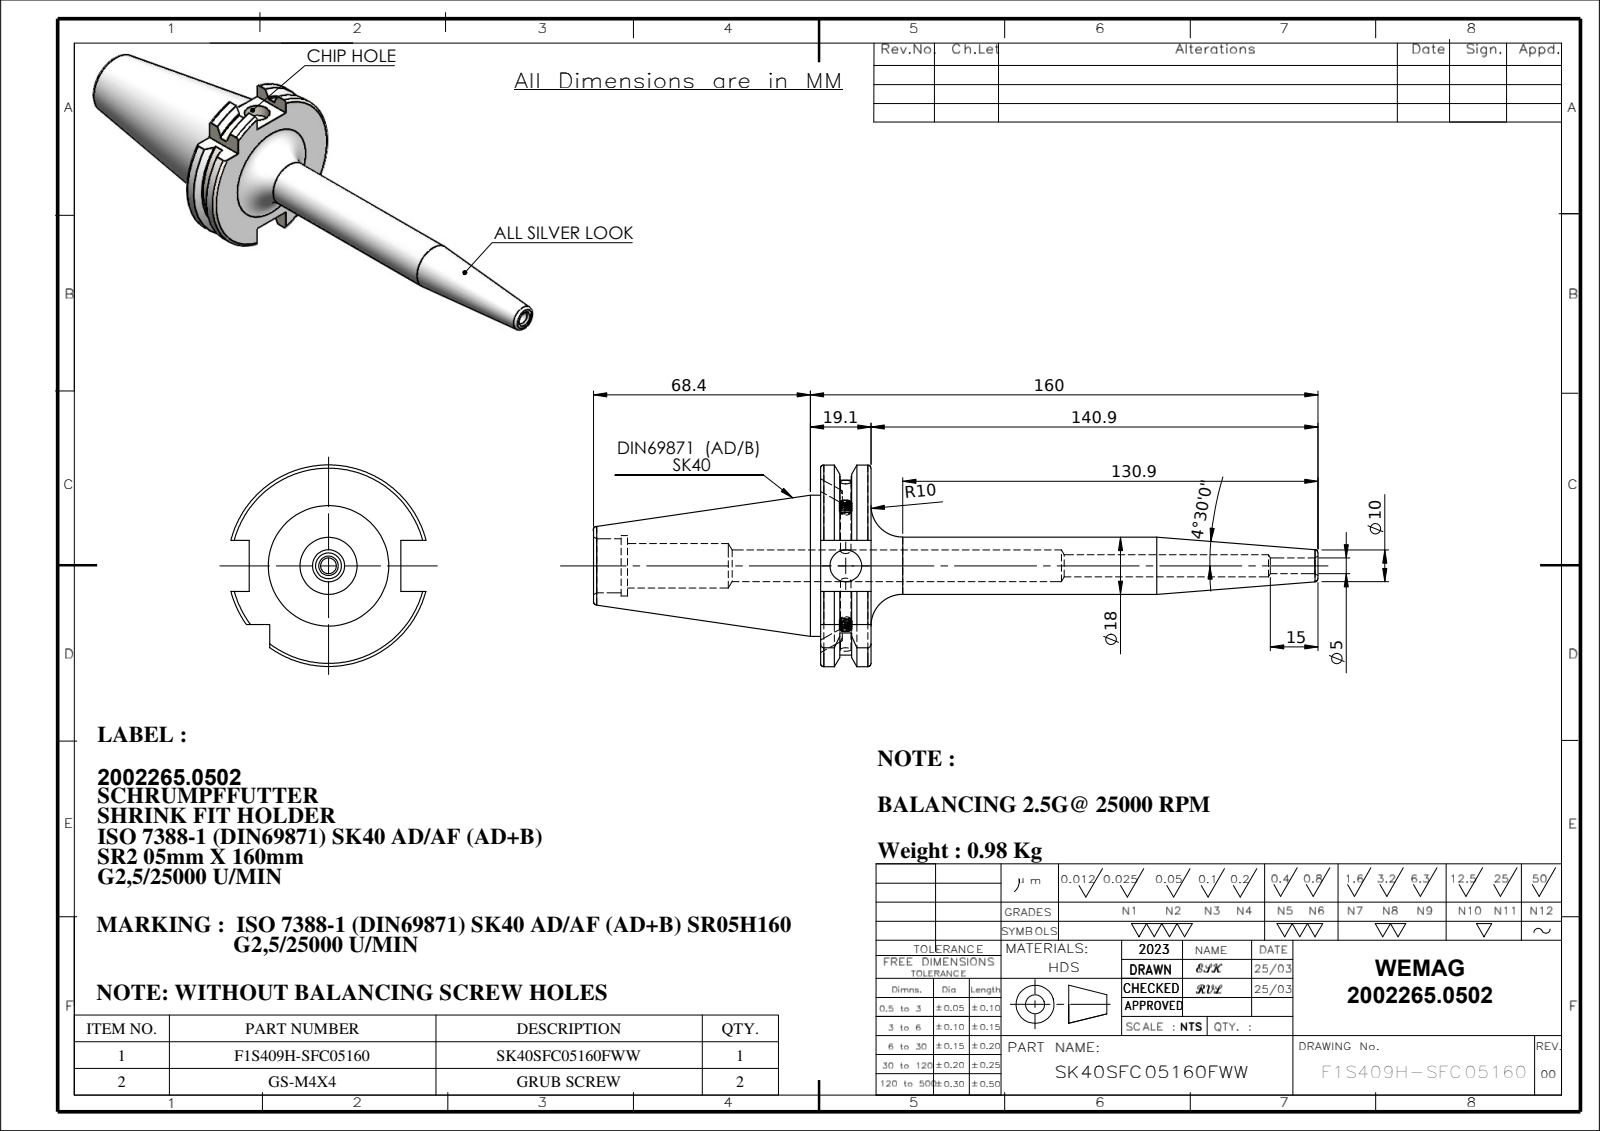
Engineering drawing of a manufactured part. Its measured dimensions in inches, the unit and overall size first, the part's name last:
Units: inches
Overall size (bounding box): 8.992 × 2.502 × 2.42
Round holes (diameter × count): ⌀0.394 ×2, ⌀0.13 ×1, ⌀0.196 ×1, ⌀0.276 ×1, ⌀0.551 ×1, ⌀0.669 ×1, ⌀0.748 ×1
Round bosses / shafts (diameter × count): ⌀0.157 ×2, ⌀1.75 ×1, ⌀0.709 ×1
Partial cylindrical surfaces — rounded edges, fillets, slot ends (radius × count): R1.107 ×1, R1.251 ×1
Main face-to-face distances: 0.626, 0.634, 1.882, 2.819, 3.445, 0.421, 2.398, 3.024, 3.056, 2.635
Volume: 7.725 in³ · Surface area: 49.08 in²
Bodies: 3 solids, 196 faces (46 planar, 54 cylindrical, 96 other)
Part name (STEP PRODUCT): SK40SFC05160FWW; 91406-SR205160; GS-M4X4_DIN 913 - M4 x 4-N
STEP written by: SolidWorks 2018 (CONFIG_CONTROL_DESIGN)
